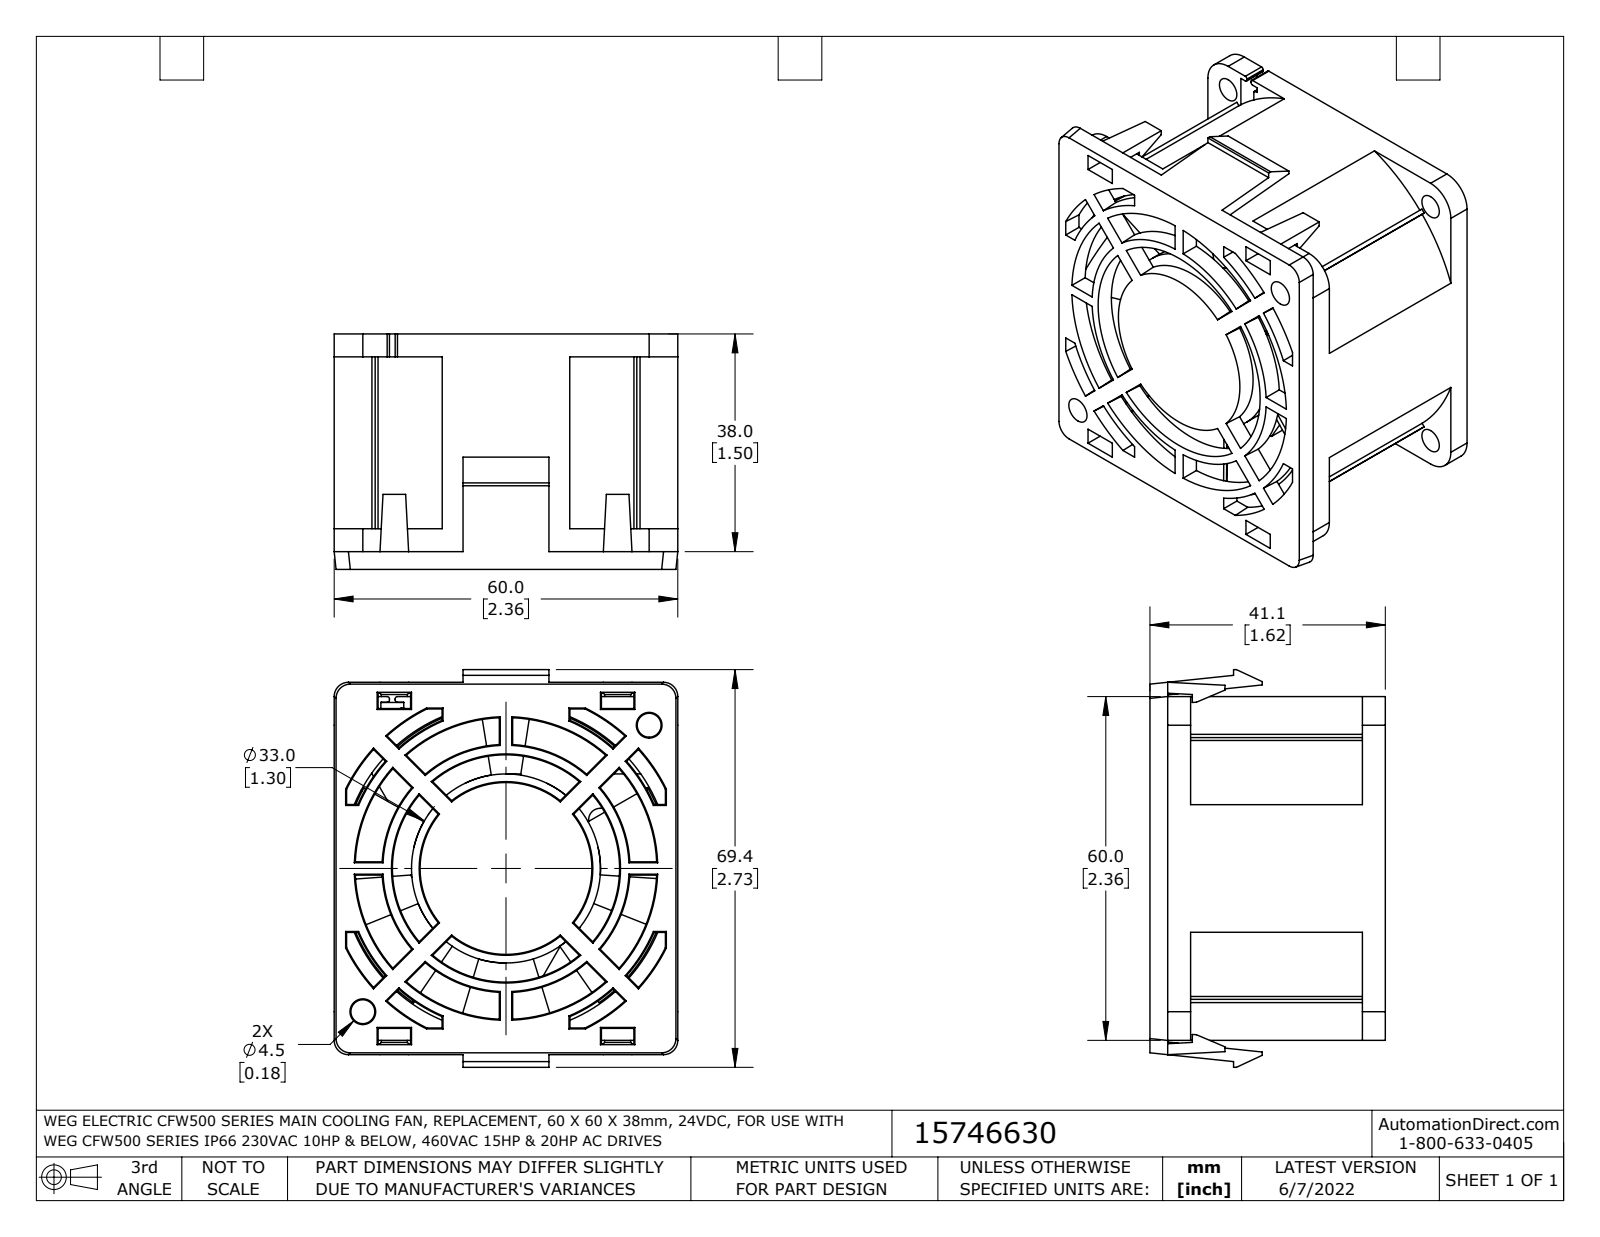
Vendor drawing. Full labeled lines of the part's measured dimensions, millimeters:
Part name (STEP PRODUCT): 15746630_CFW500_66_FAN_B nc coord
STEP written by: SolidWorks 2021 (AUTOMOTIVE_DESIGN)
Units: millimetres
Bodies: 1 solid, 349 faces (227 planar, 74 cylindrical, 48 other)
Overall size (bounding box): 69.4 × 60 × 41.1
Volume: 66 630 mm³ · Surface area: 37 180 mm²
Round holes (diameter × count): ⌀4.3 ×4, ⌀57.5 ×1
Round bosses / shafts (diameter × count): ⌀33 ×1
Partial cylindrical surfaces — rounded edges, fillets, slot ends (radius × count): R16.5 ×7, R28.5 ×7, R0.4 ×5, R2.5 ×4, R5 ×4, R2 ×3, R32 ×1
Main face-to-face distances: 60, 19, 41.1, 0.5, 38, 3.1, 17, 22.1, 15, 2
Hole centre spacings: 35.4, 50, 70.7
